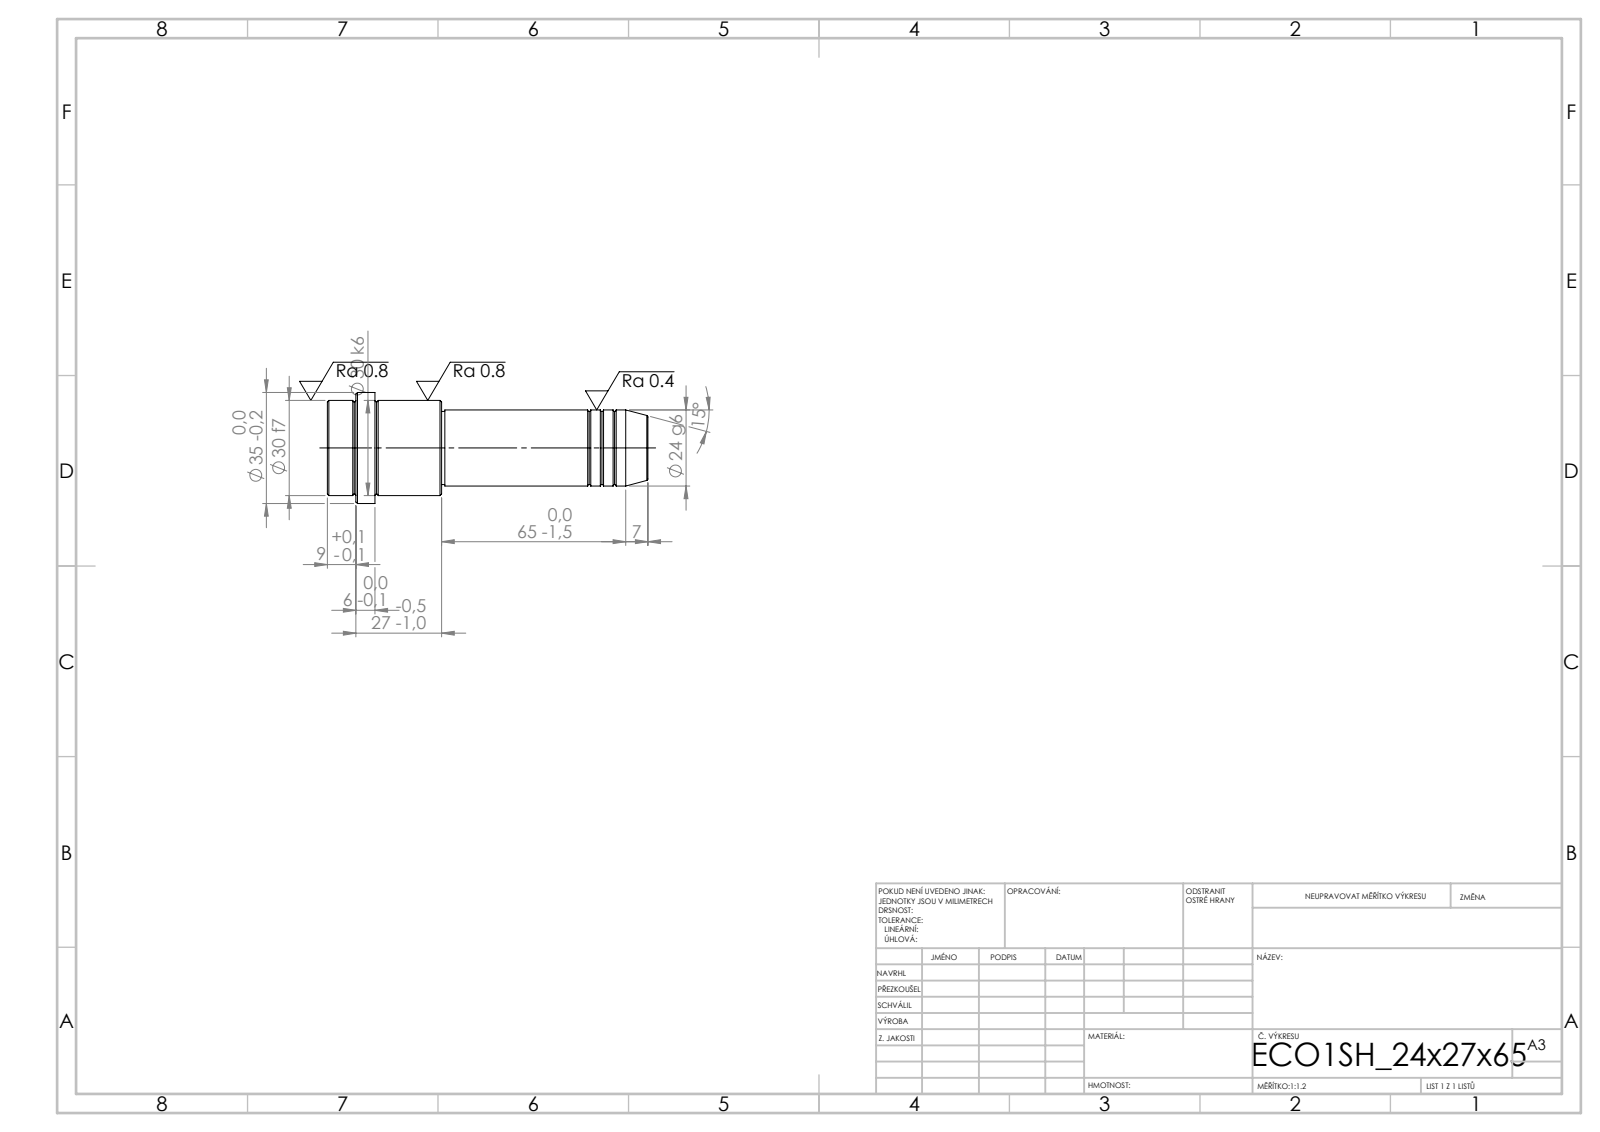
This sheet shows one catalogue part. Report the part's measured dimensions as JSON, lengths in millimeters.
{"step_written_by": "SolidWorks 2019 (CONFIG_CONTROL_DESIGN)", "units": "millimeters", "bodies": {"solids": 1, "faces": 52, "planar": 6, "cylindrical": 16, "other": 30}, "overall_size": [101, 35, 35], "volume_mm3": 55679, "surface_area_mm2": 10354, "round_bosses_or_shafts": [[35, 1], [30, 1], [24, 1], [23, 1]], "face_to_face_distances": [101, 86, 15, 65, 21, 36, 92, 27, 6, 9]}
